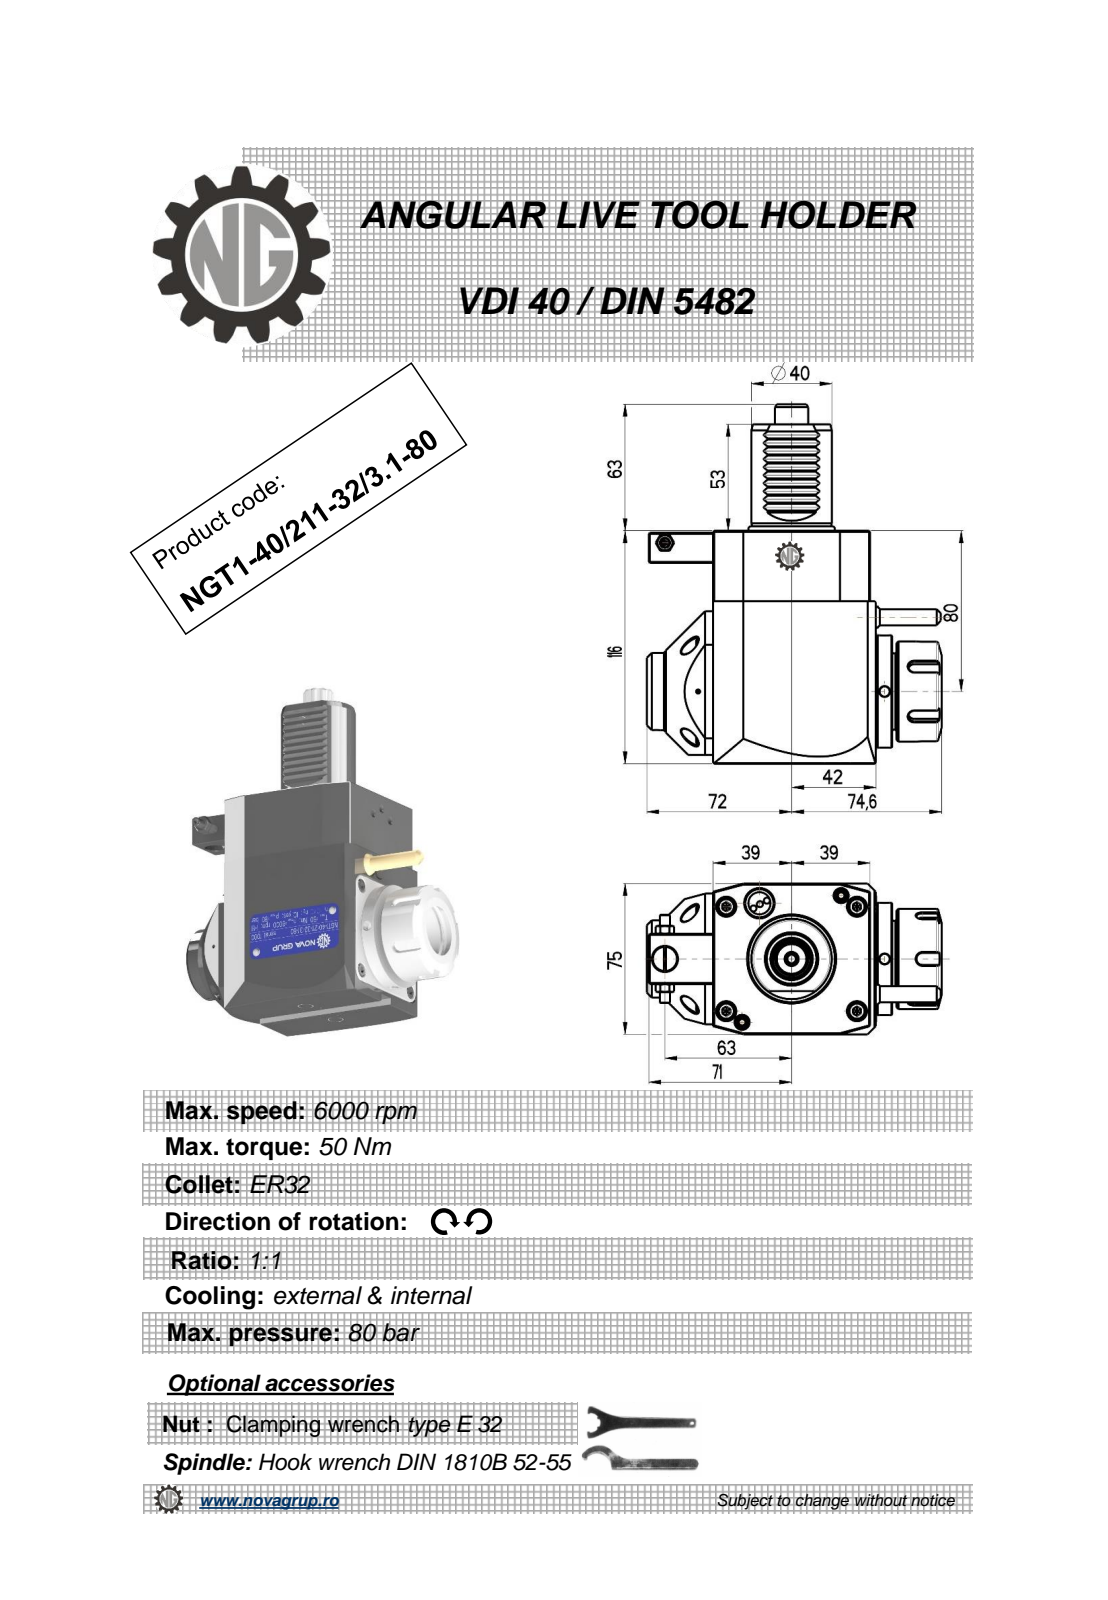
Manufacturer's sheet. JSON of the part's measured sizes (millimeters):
{"part_name": "NGT1_40_211_32_3_1_80", "step_written_by": "PRO/ENGINEER BY PARAMETRIC TECHNOLOGY CORPORATION, 2010280 (CONFIG_CONTROL_DESIGN)", "units": "millimeters", "bodies": {"solids": 1, "faces": 461, "planar": 183, "cylindrical": 124, "other": 154}, "overall_size": [179, 146.6, 75], "volume_mm3": 900795, "surface_area_mm2": 72210, "round_holes": [[5, 3], [4.2, 2], [3, 1], [5.3, 1], [9.5, 1], [12, 1], [27, 1]], "round_bosses_or_shafts": [[56, 1], [50, 1], [43, 1], [40, 1], [38.5, 1], [11.2, 1], [8.96, 1], [8, 1]], "partial_cylinders_radius": [[3.03, 18], [0.26, 12], [0.3, 10], [0.22, 6], [3, 5], [0.5, 1], [6.75, 1], [8.25, 1]], "face_to_face_distances": [75, 116, 81, 78, 3, 111, 80.8, 2.8, 7.5, 0.5], "hole_center_spacings": [39.58, 40.93, 46.25, 63, 72.5, 109.25, 131.95]}
